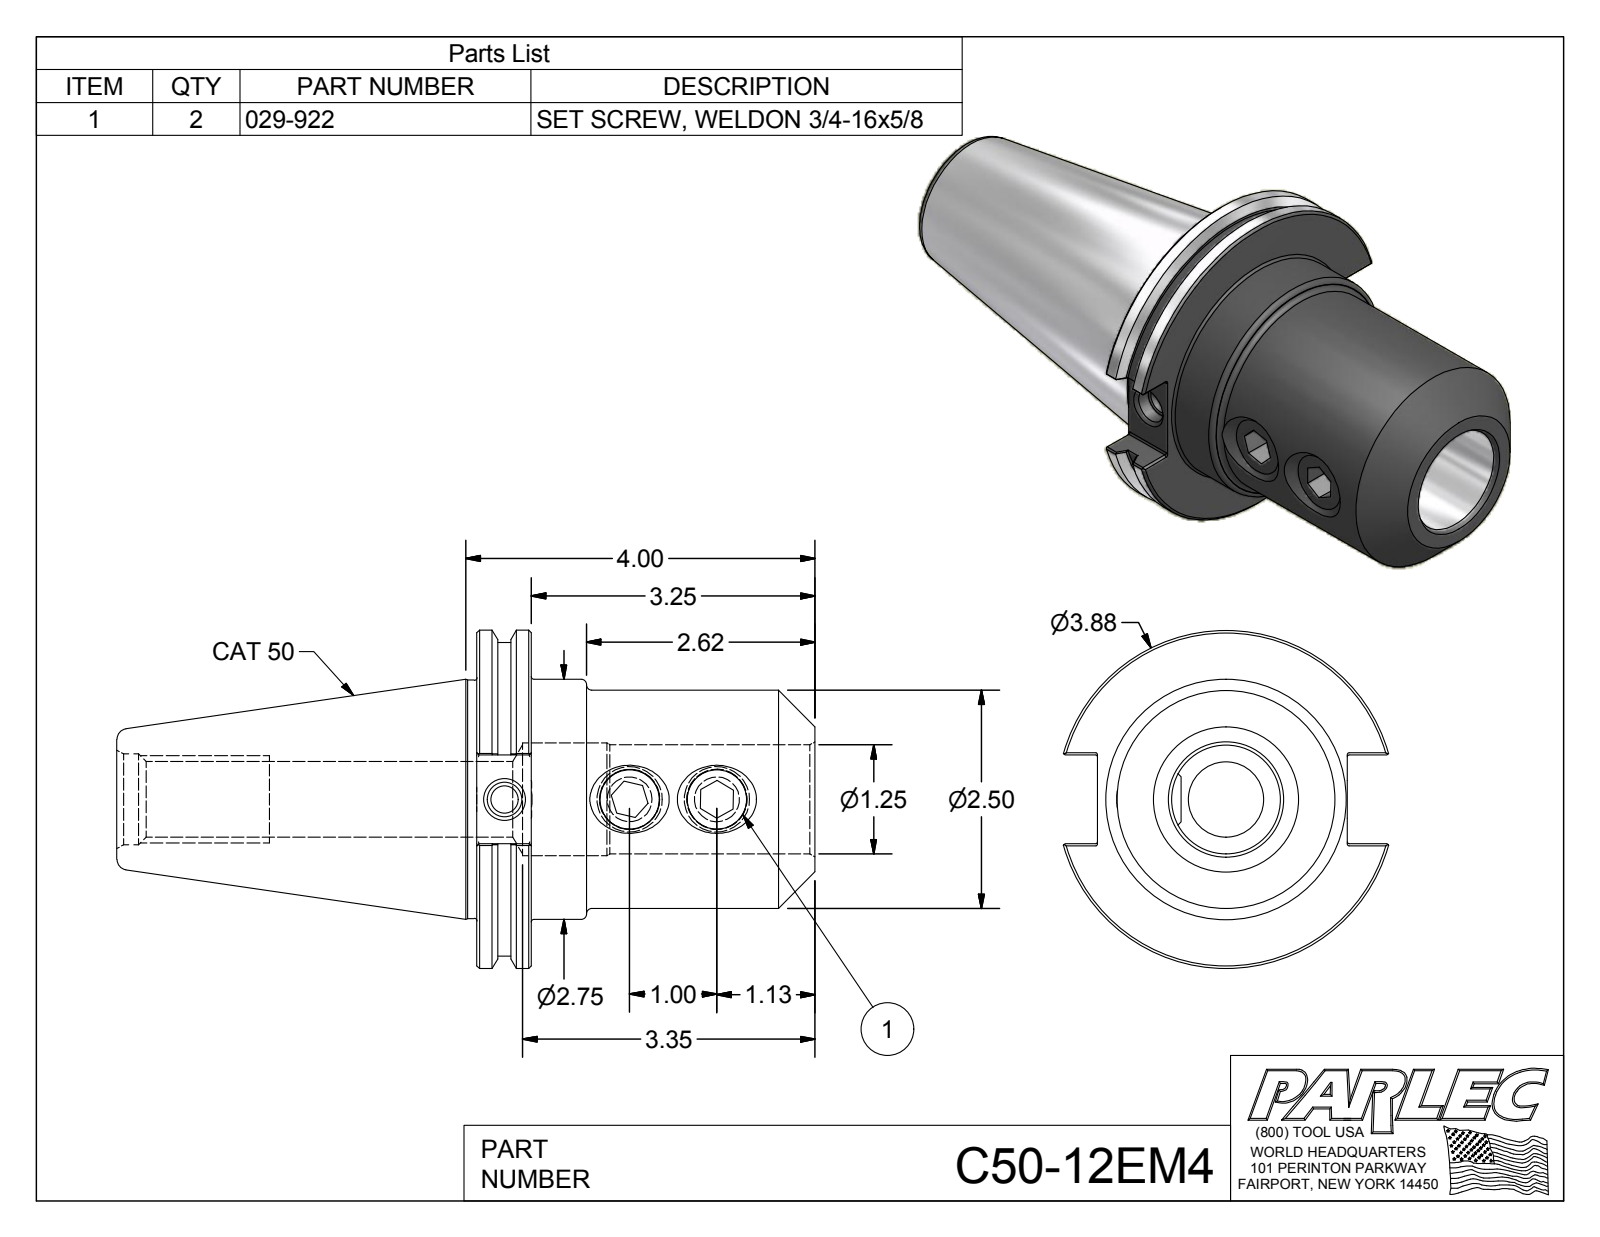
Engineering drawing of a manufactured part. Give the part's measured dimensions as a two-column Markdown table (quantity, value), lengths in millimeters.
| quantity | value |
| --- | --- |
| part name | C50-12EM4; C50-12EM4-1; 029-922 |
| STEP written by | Autodesk Inventor 2012 (AUTOMOTIVE_DESIGN) |
| units | millimeters |
| bodies | 3 solids, 119 faces (51 planar, 31 cylindrical, 37 other) |
| overall size | 203.2 × 98.4 × 94.7 |
| volume | 510 300 mm³ |
| surface area | 71 290 mm² |
| round holes (diameter × count) | 17.3 × 2, 8 × 1, 10.1 × 1, 22 × 1, 26.4 × 1, 31.8 × 1, 32.8 × 1 |
| round bosses / shafts (diameter × count) | 19.1 × 2, 98.4 × 1, 91.3 × 1, 69.9 × 1, 69.3 × 1, 63.5 × 1 |
| partial cylindrical surfaces (radius × count) | 0.5 × 12 |
| main face-to-face distances | 15.9, 98.4, 82.6, 64.2, 104.8, 120.7, 203.2, 72.6, 8.5, 48.3 |
| hole center spacings | 25.4, 36.4, 61.8 |
